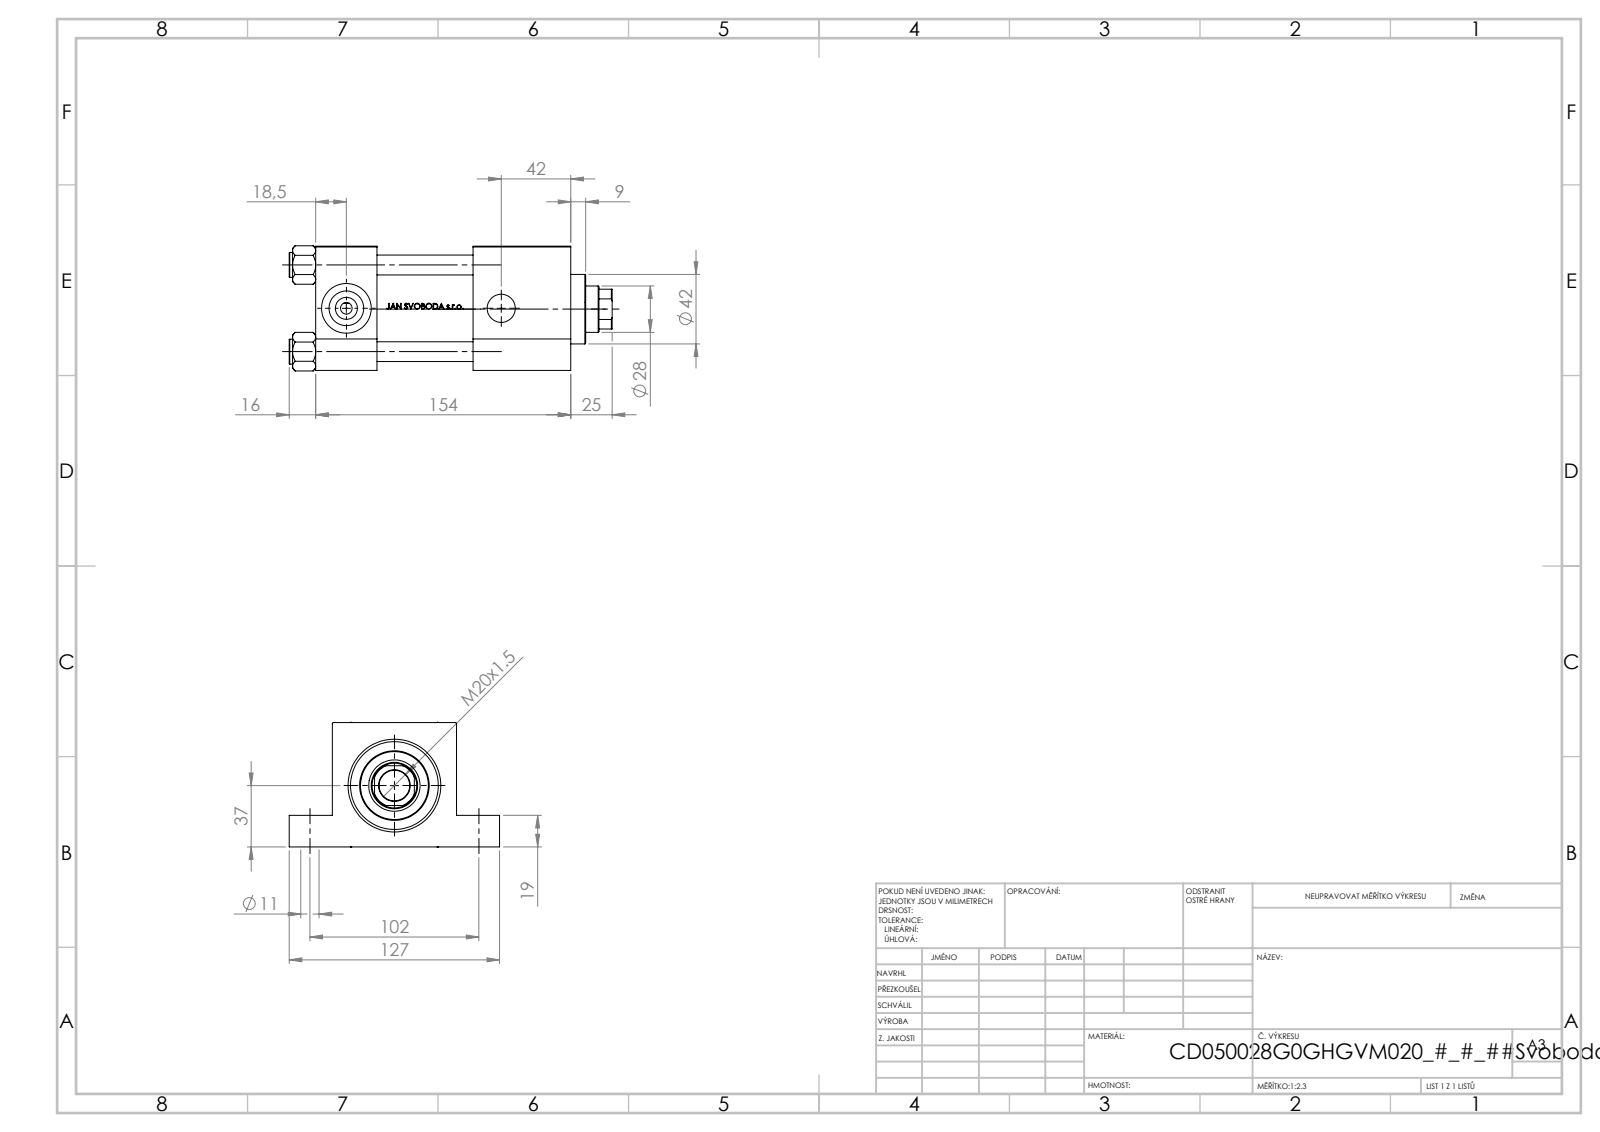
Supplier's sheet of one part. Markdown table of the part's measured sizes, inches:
| quantity | value |
| --- | --- |
| part name | V215CD_VCP_G; V215CD_G_Body; V215CD_NUT_M5_G; V215CD_VC_G (+1 more) |
| STEP written by | SolidWorks 2019 (CONFIG_CONTROL_DESIGN) |
| units | inches |
| bodies | 11 solids, 1087 faces (431 planar, 124 cylindrical, 532 other) |
| overall size | 7.677 × 5 × 2.974 |
| volume | 46.87 in³ |
| surface area | 253 in² |
| round holes (diameter × count) | 0.433 × 4, 0.472 × 4, 0.276 × 2, 0.825 × 2, 0.669 × 1, 0.728 × 1, 1.102 × 1, 1.181 × 1, 1.22 × 1, 1.614 × 1, 1.969 × 1, 2.087 × 1 |
| round bosses / shafts (diameter × count) | 0.591 × 4, 2.205 × 1, 1.654 × 1 |
| partial cylindrical surfaces (radius × count) | 0.531 × 1 |
| main face-to-face distances | 2.953, 1.457, 6.063, 4.606, 0.748, 2.205, 3.74, 2.283, 2.323, 1.024 |
| hole center spacings | 2.059, 1.442, 1.47, 2.912, 4.016, 4.409, 5.964, 3.681 |
